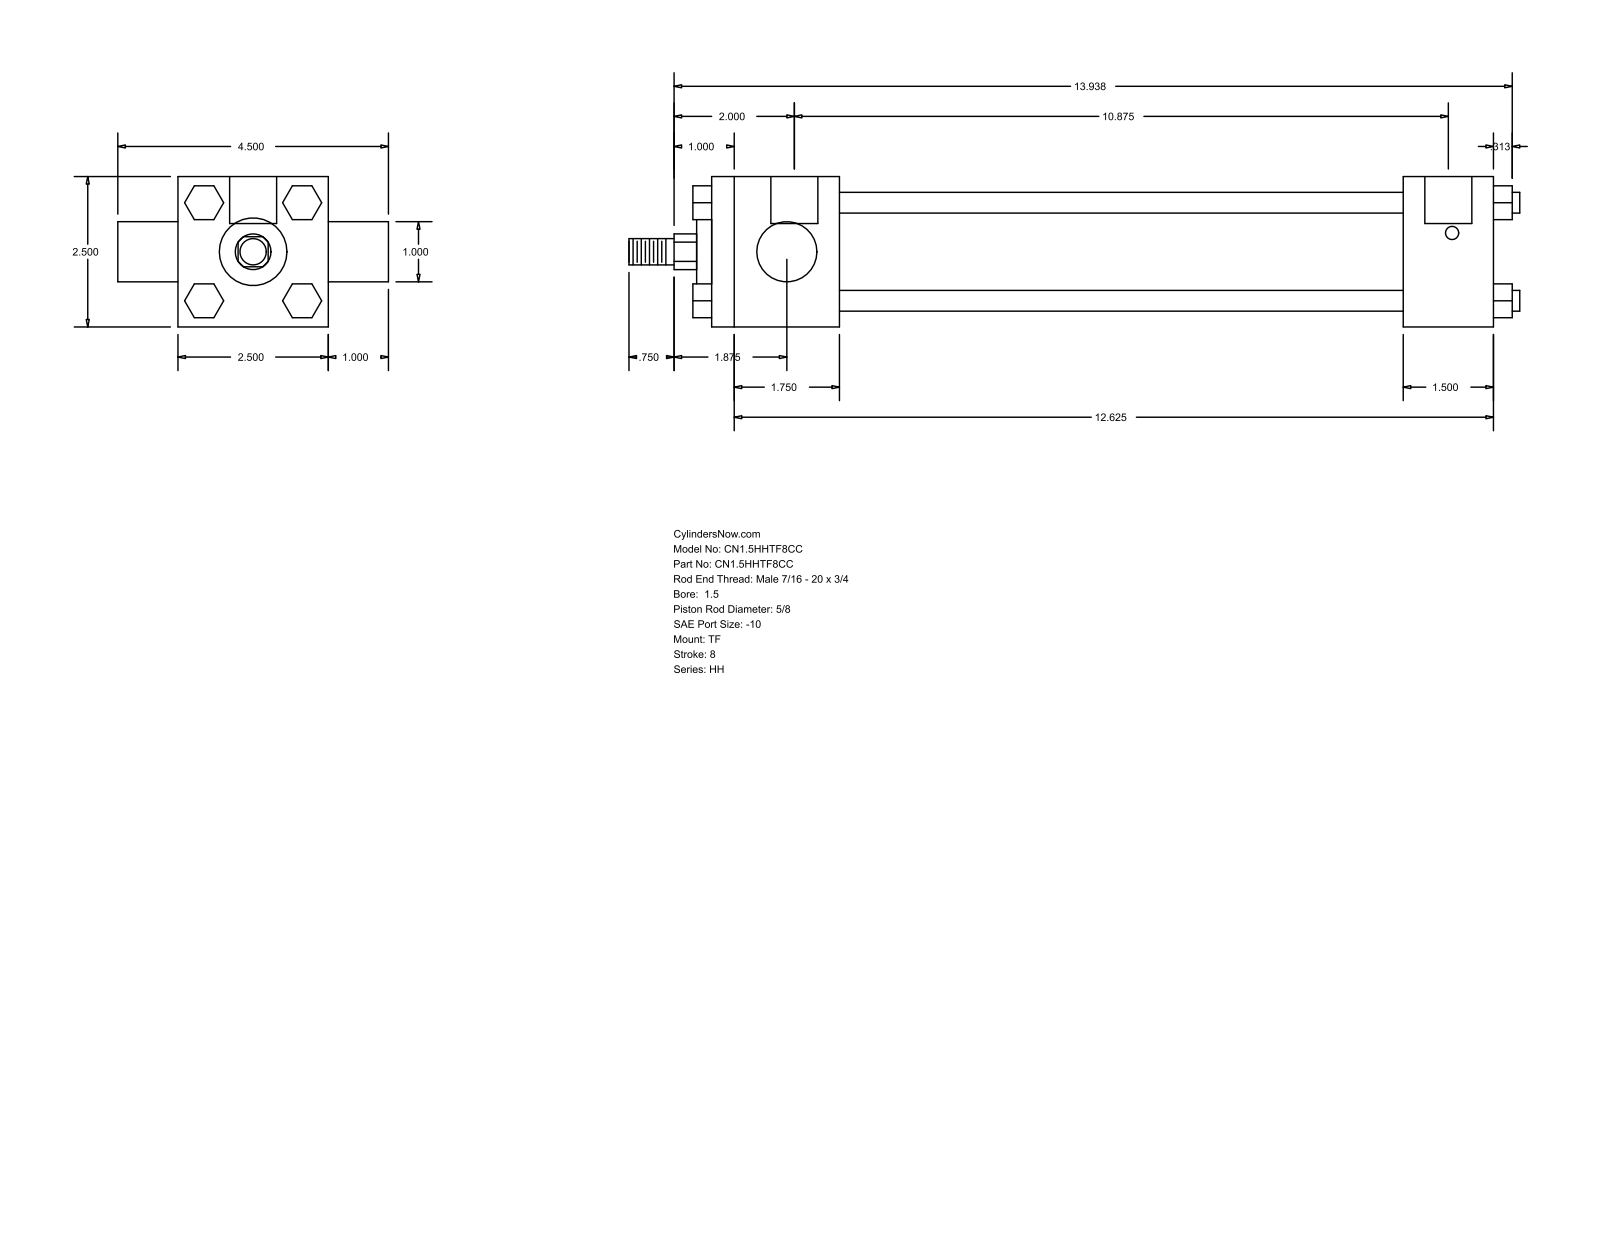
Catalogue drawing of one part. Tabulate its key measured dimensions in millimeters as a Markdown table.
| quantity | value |
| --- | --- |
| part name | HH_TF__0150_0.625 |
| STEP written by | GSSL Pune (CONFIG_CONTROL_DESIGN) |
| units | millimeters |
| bodies | 0 solids, 120 faces (92 planar, 28 cylindrical, 0 other) |
| overall size | 376.24 × 114.3 × 63.5 |
| round holes (diameter × count) | 5.56 × 3, 19.84 × 2 |
| round bosses / shafts (diameter × count) | 8.76 × 4, 44.45 × 1, 28.57 × 1, 25.4 × 1, 15.88 × 1, 11.11 × 1 |
| partial cylindrical surfaces (radius × count) | 7.54 × 1 |
| main face-to-face distances | 63.5, 330.19, 53.97, 276.22, 292.1, 238.13, 38.09, 25.4, 88.9, 20.7 |
| hole center spacings | 1.59, 277.81, 276.22, 279.4 |
